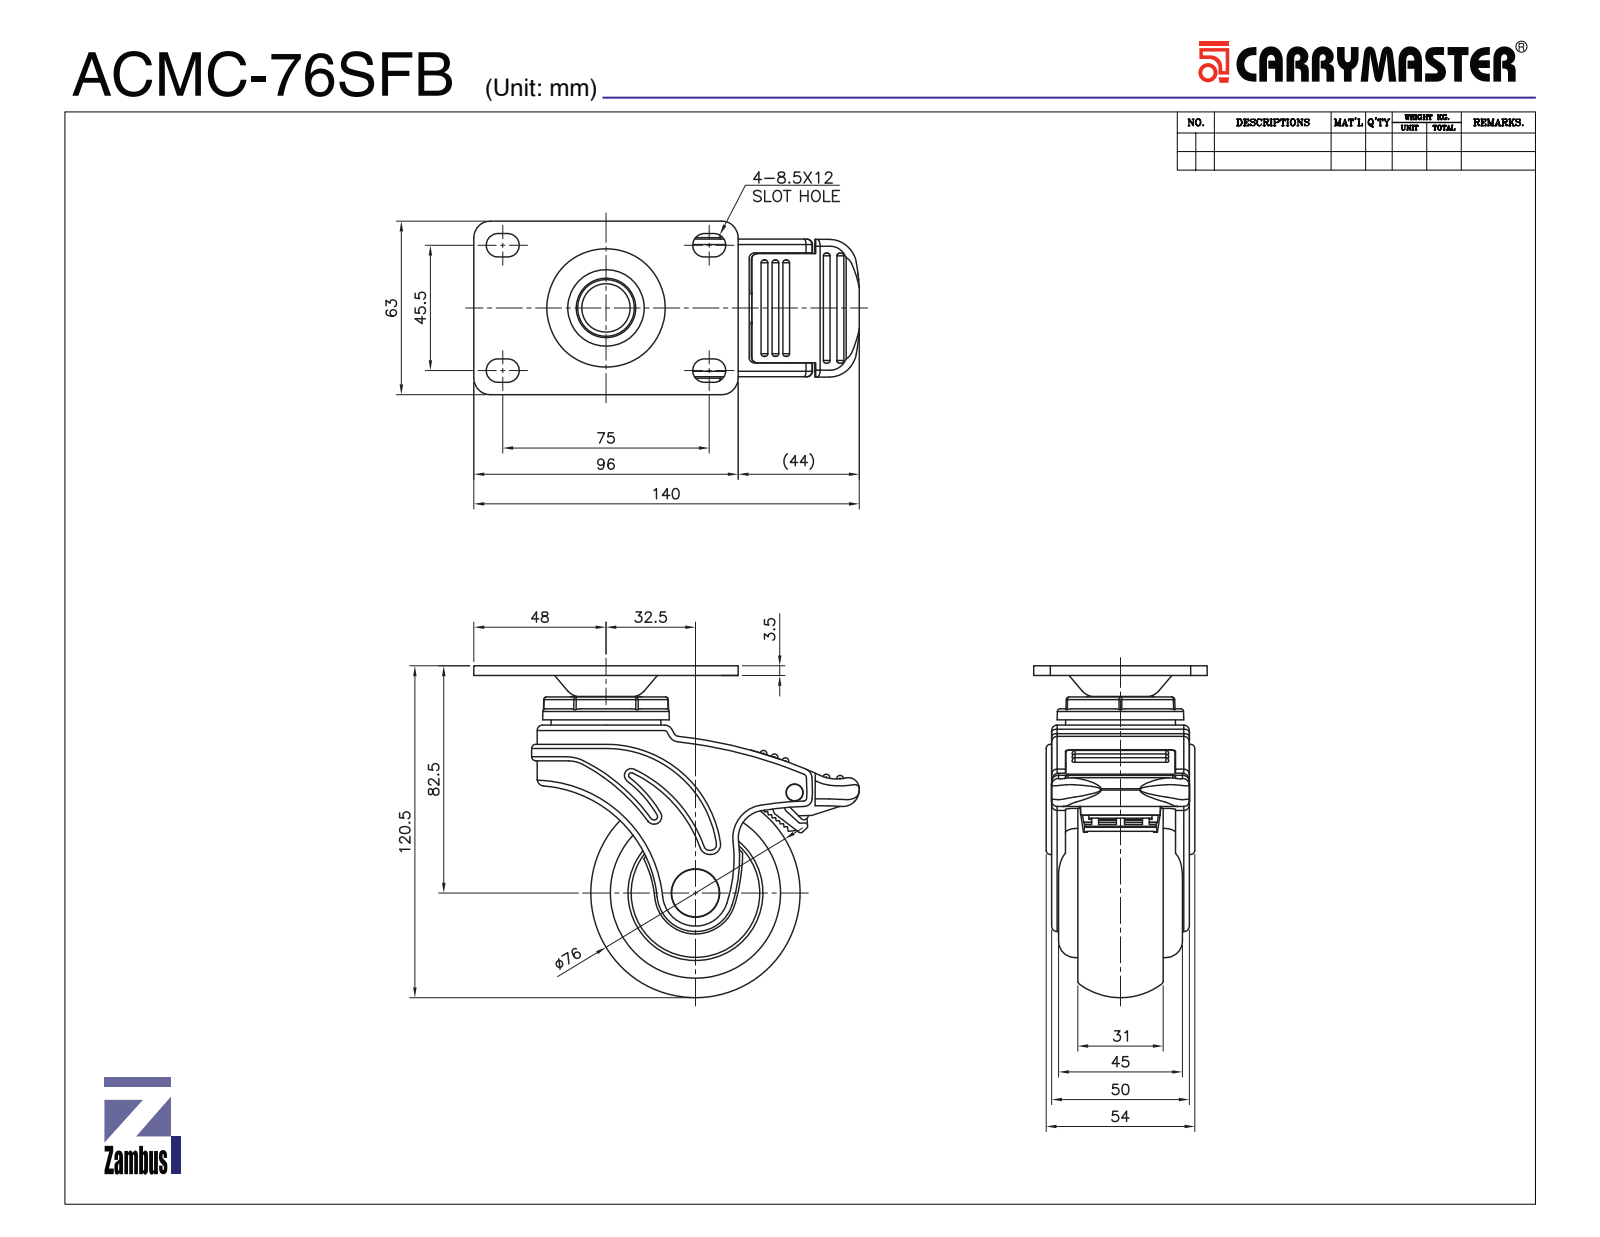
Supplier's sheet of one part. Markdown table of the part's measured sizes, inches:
| quantity | value |
| --- | --- |
| part name | ACMC-76 WHEEL; ACMC-76 BRAKE FRAME; ACMC-76 BRAKE; ACMC-76 F TOP PLATE (+2 more) |
| STEP written by | SolidWorks 2019 (CONFIG_CONTROL_DESIGN) |
| units | inches |
| bodies | 5 solids, 591 faces (218 planar, 215 cylindrical, 158 other) |
| overall size | 5.512 × 4.724 × 2.48 |
| volume | 16.55 in³ |
| surface area | 115.9 in² |
| round holes (diameter × count) | 0.681 × 1, 1.287 × 1, 1.969 × 1, 2.441 × 1 |
| round bosses / shafts (diameter × count) | 2.441 × 1, 1.844 × 1, 1.575 × 1, 0.709 × 1, 0.669 × 1, 0.236 × 1 |
| partial cylindrical surfaces (radius × count) | 0.02 × 24, 0.039 × 16, 0.079 × 14, 0.167 × 8, 0.049 × 5, 0.059 × 5, 0.098 × 4, 0.236 × 4 |
| main face-to-face distances | 0.197, 1.772, 0.177, 1.575, 0.138, 0.63, 0.374, 1.398, 0.768, 1.594 |
